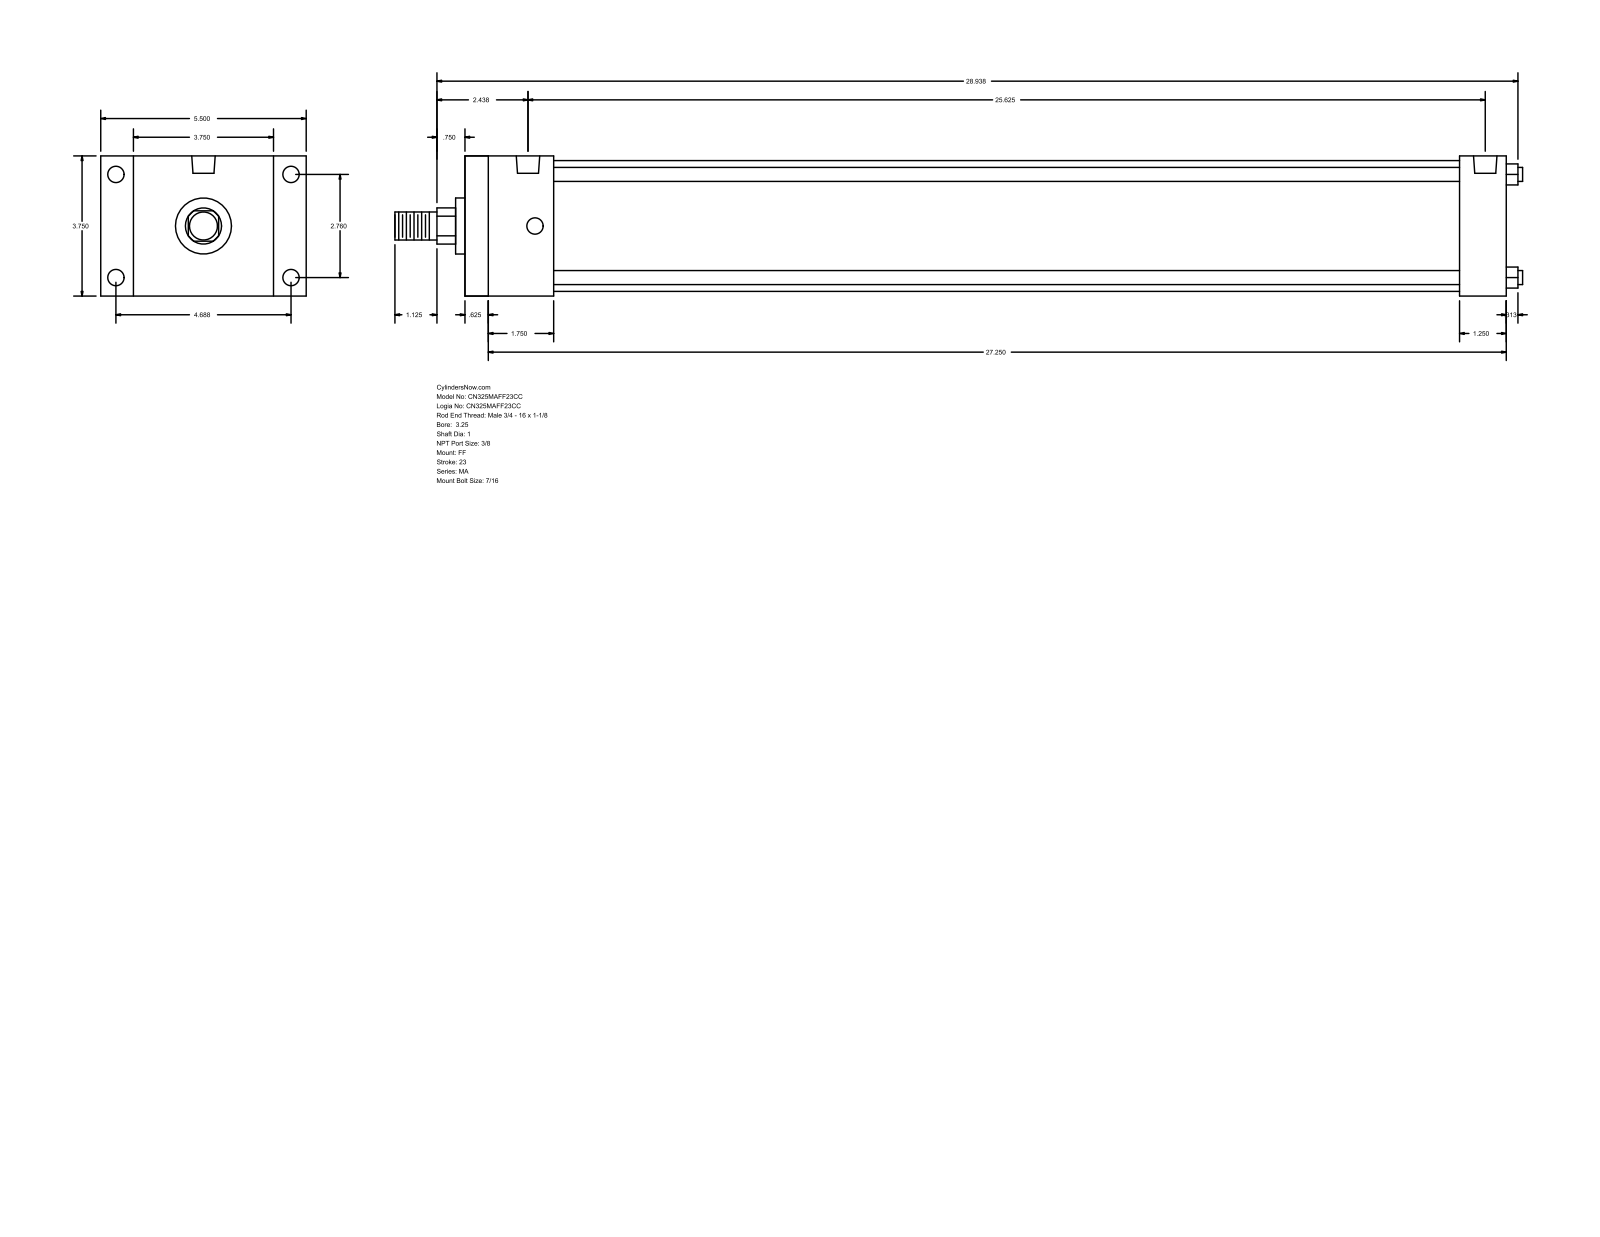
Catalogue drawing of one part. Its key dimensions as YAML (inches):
part_name: "MA_FF__0325_1"
step_written_by: "GSSL Pune (CONFIG_CONTROL_DESIGN)"
units: inches
bodies: {solids: 0, faces: 92, planar: 64, cylindrical: 28, other: 0}
overall_size: [30.187, 5.5, 3.75]
round_holes:
  - {diameter: 0.437, count: 8}
  - {diameter: 0.627, count: 2}
round_bosses_or_shafts:
  - {diameter: 0.375, count: 4}
  - {diameter: 3.5, count: 1}
  - {diameter: 1.5, count: 1}
  - {diameter: 1, count: 1}
  - {diameter: 0.75, count: 1}
partial_cylinders:
  - {radius: 0.484, count: 1}
face_to_face_distances: [3.75, 27.875, 0.625, 27.25, 0.875, 4.625, 2.375, 26.625, 1.75, 26]
hole_center_spacings: [2.76, 4.687, 5.439, 25.25, 0.187, 0.188, 25.437, 25.438]
